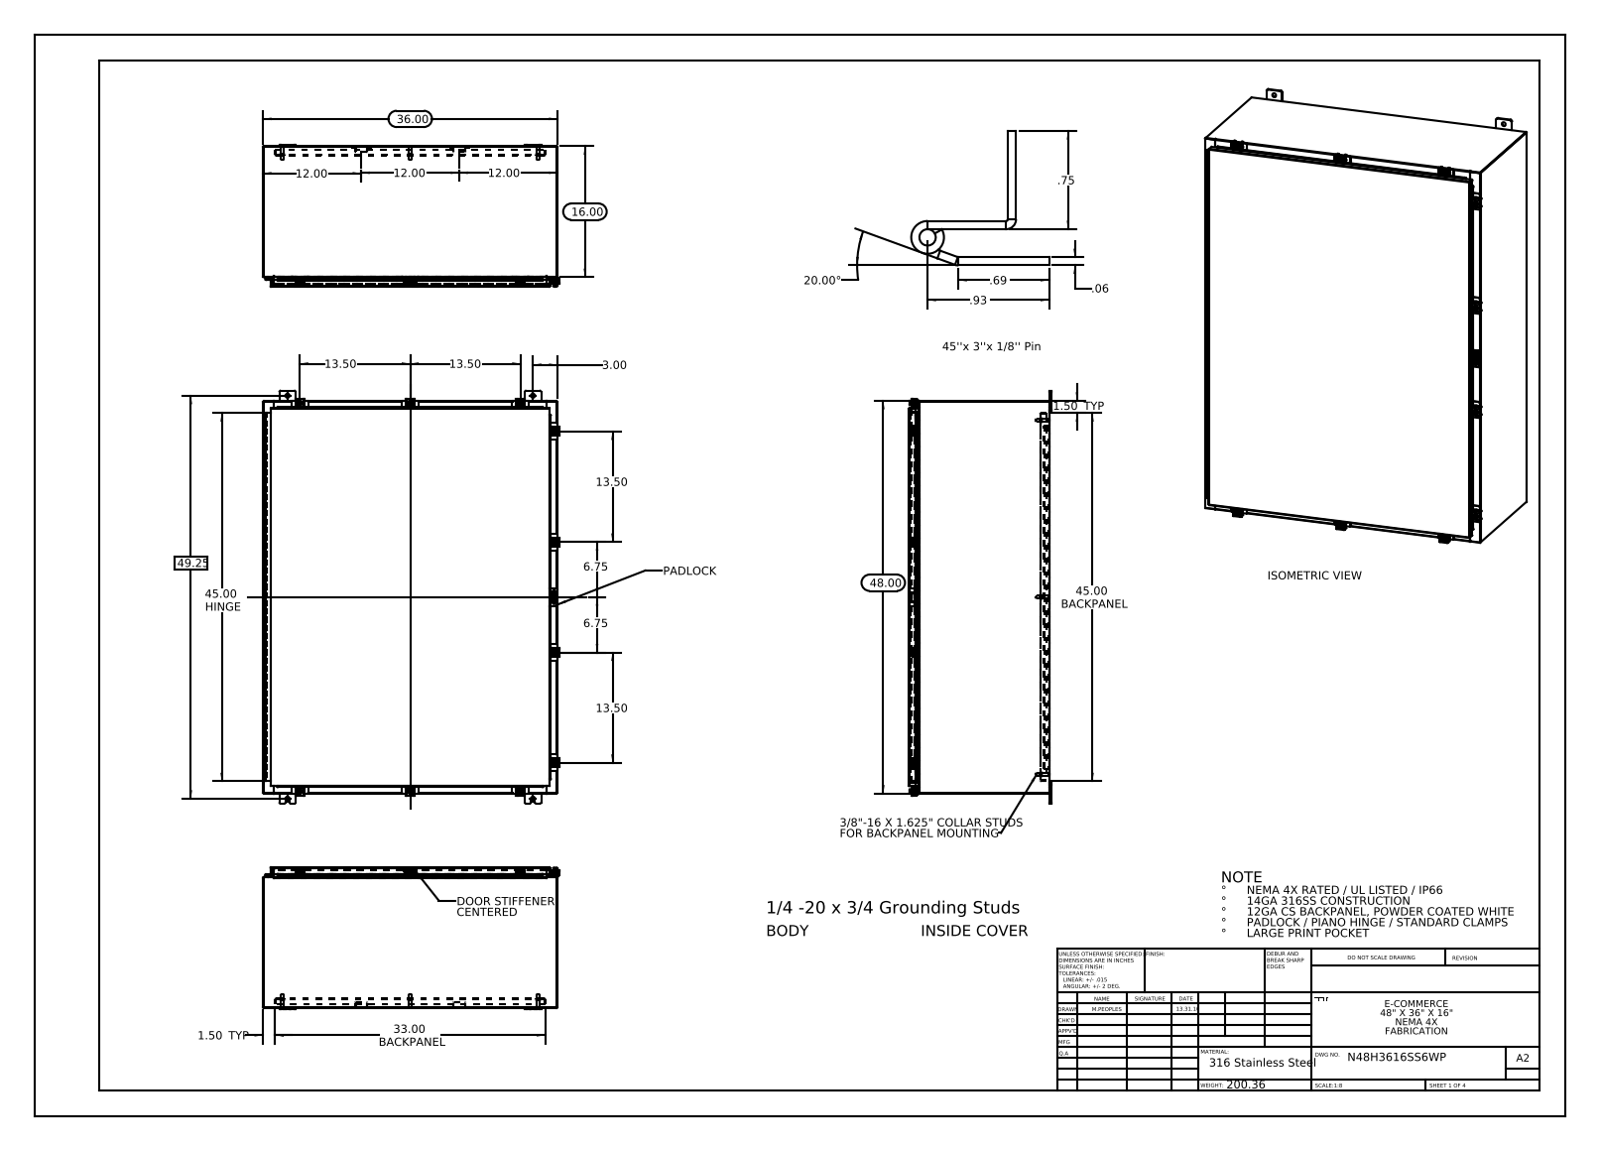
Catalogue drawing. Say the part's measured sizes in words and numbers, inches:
The part is named "N48H3616SS6WP; N48H3616SS6WP Mounting Feet; N48H3616SS6WP Enclosure Stiffener; N48H3616SS6WP Clamp Top (+8 more)". Its 3-D file was written by "SolidWorks 2013 (CONFIG_CONTROL_DESIGN)". It is 74 solids with 2999 faces: 1562 planar, 1269 cylindrical and 168 other. Overall it measures 50.5 by 36.211 by 17.389 inches. Its volume is 700.8 cubic inches and its surface area 17 600 square inches. Round holes: 12 of diameter 0.5, 10 of diameter 0.213, 10 of diameter 0.26, 6 of diameter 0.25, 2 of diameter 0.125, 1 of diameter 0.125. Round bosses or shafts: 11 of diameter 0.25, 10 of diameter 0.5, 10 of diameter 0.399, 8 of diameter 0.625, 8 of diameter 0.375, 8 of diameter 0.33. Partial cylindrical surfaces (rounded edges, fillets, slot ends): 46 of radius 0.06, 39 of radius 0.013, 33 of radius 0.088, 24 of radius 0.19, 20 of radius 0.12, 20 of radius 0.141, 15 of radius 0.05, 14 of radius 0.08. The main face-to-face distances are 0.075, 17.126, 17.051, 0.104, 17.201, 35.925, 1, 16.126, 1.075, 16.051. The hole center spacings are 13.5, 13.663, 20, 20.123, 21.625, 23.82, 27, 38.003.
